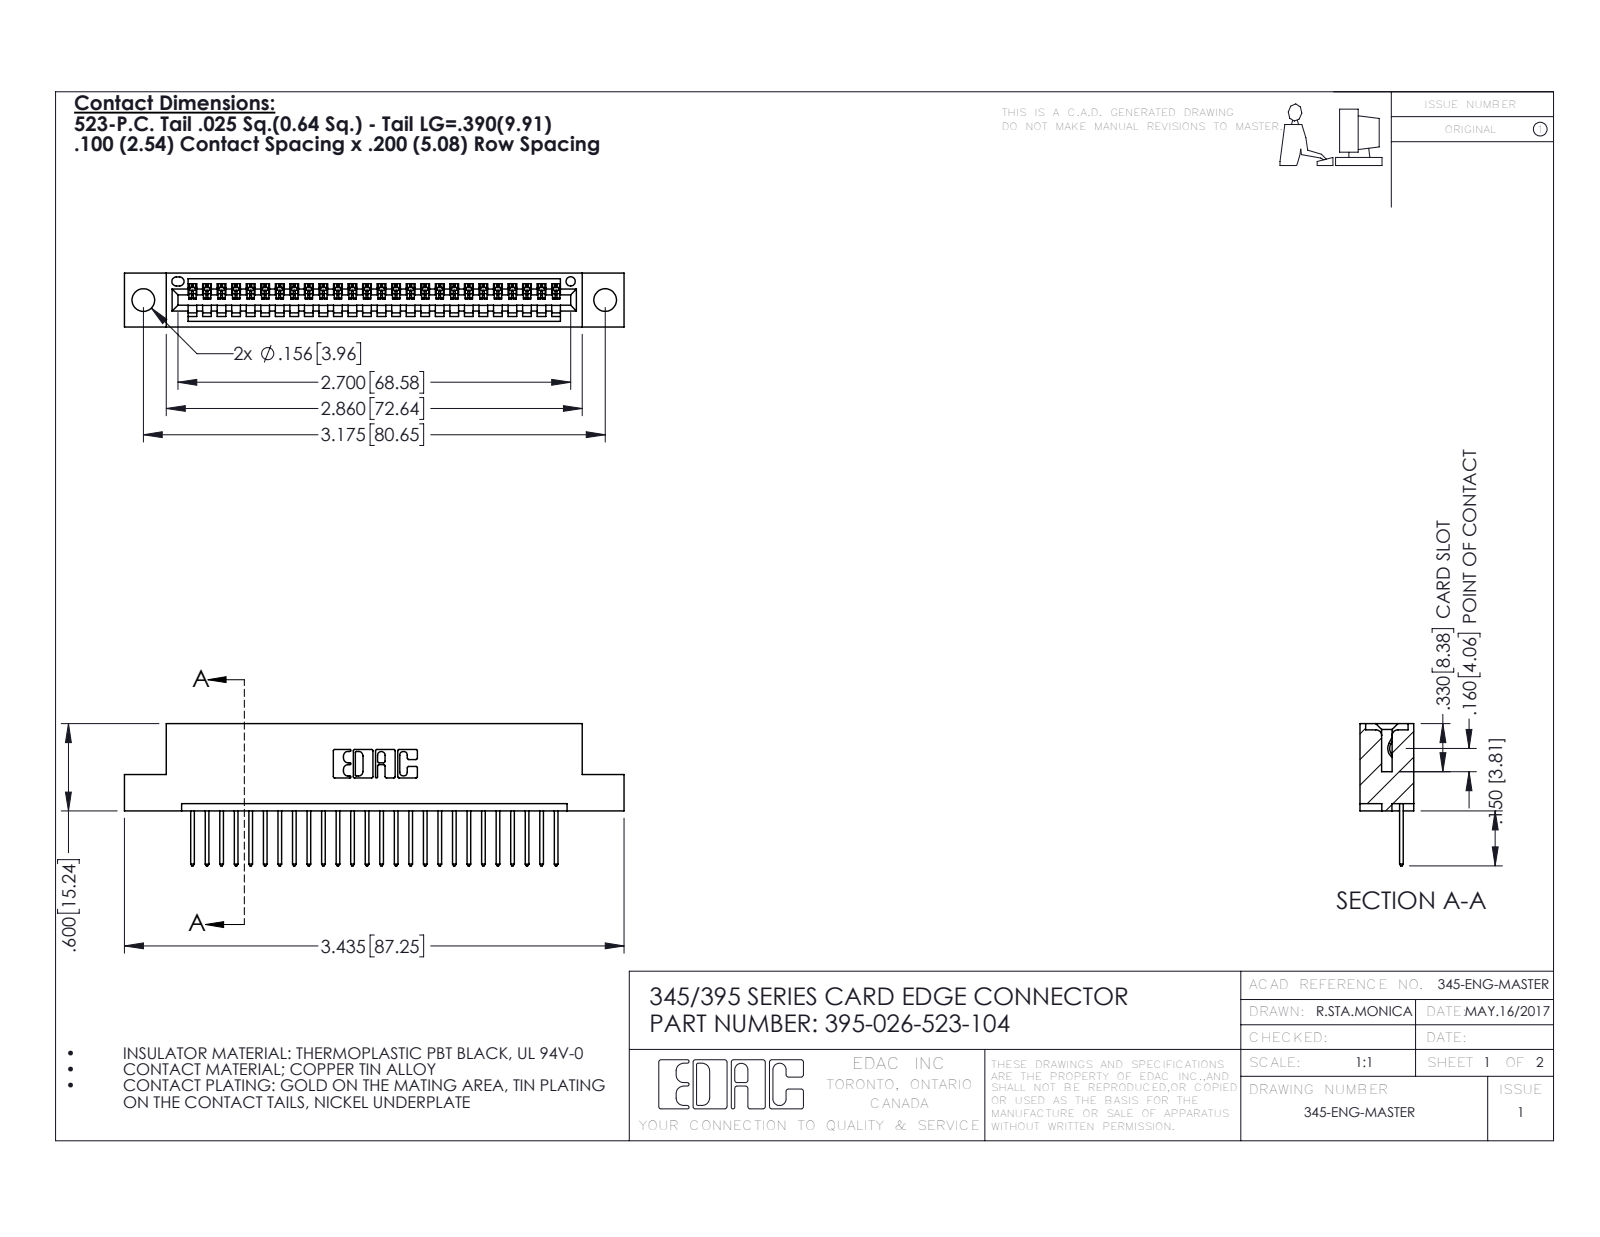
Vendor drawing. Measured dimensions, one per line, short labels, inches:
name: 345-292-001_345-293-123; 345 Part_Flush Mounting Lugs - 0.156 Dia-TH; 395-026-523-104
written by: SolidWorks 2016 (CONFIG_CONTROL_DESIGN)
unit: in
bodies: 27 solids, 1634 faces (1120 planar, 514 cylindrical, 0 other)
size: 3.435 × 0.977 × 0.37
volume: 0.492 in³; area: 16.01 in²
holes: 2× ⌀0.156, 1× ⌀0.064
rounds: 52× R0.006, 52× R0.01, 22× R0.01, 6× R0.007, 6× R0.031, 3× R0.026, 2× R0.031, 2× R0.04
face distances: 0.298, 0.072, 0.2, 0.37, 0.098, 0.272, 0.025, 0.225, 0.149, 0.072
hole spacings: 0.27, 2.94, 3.175
